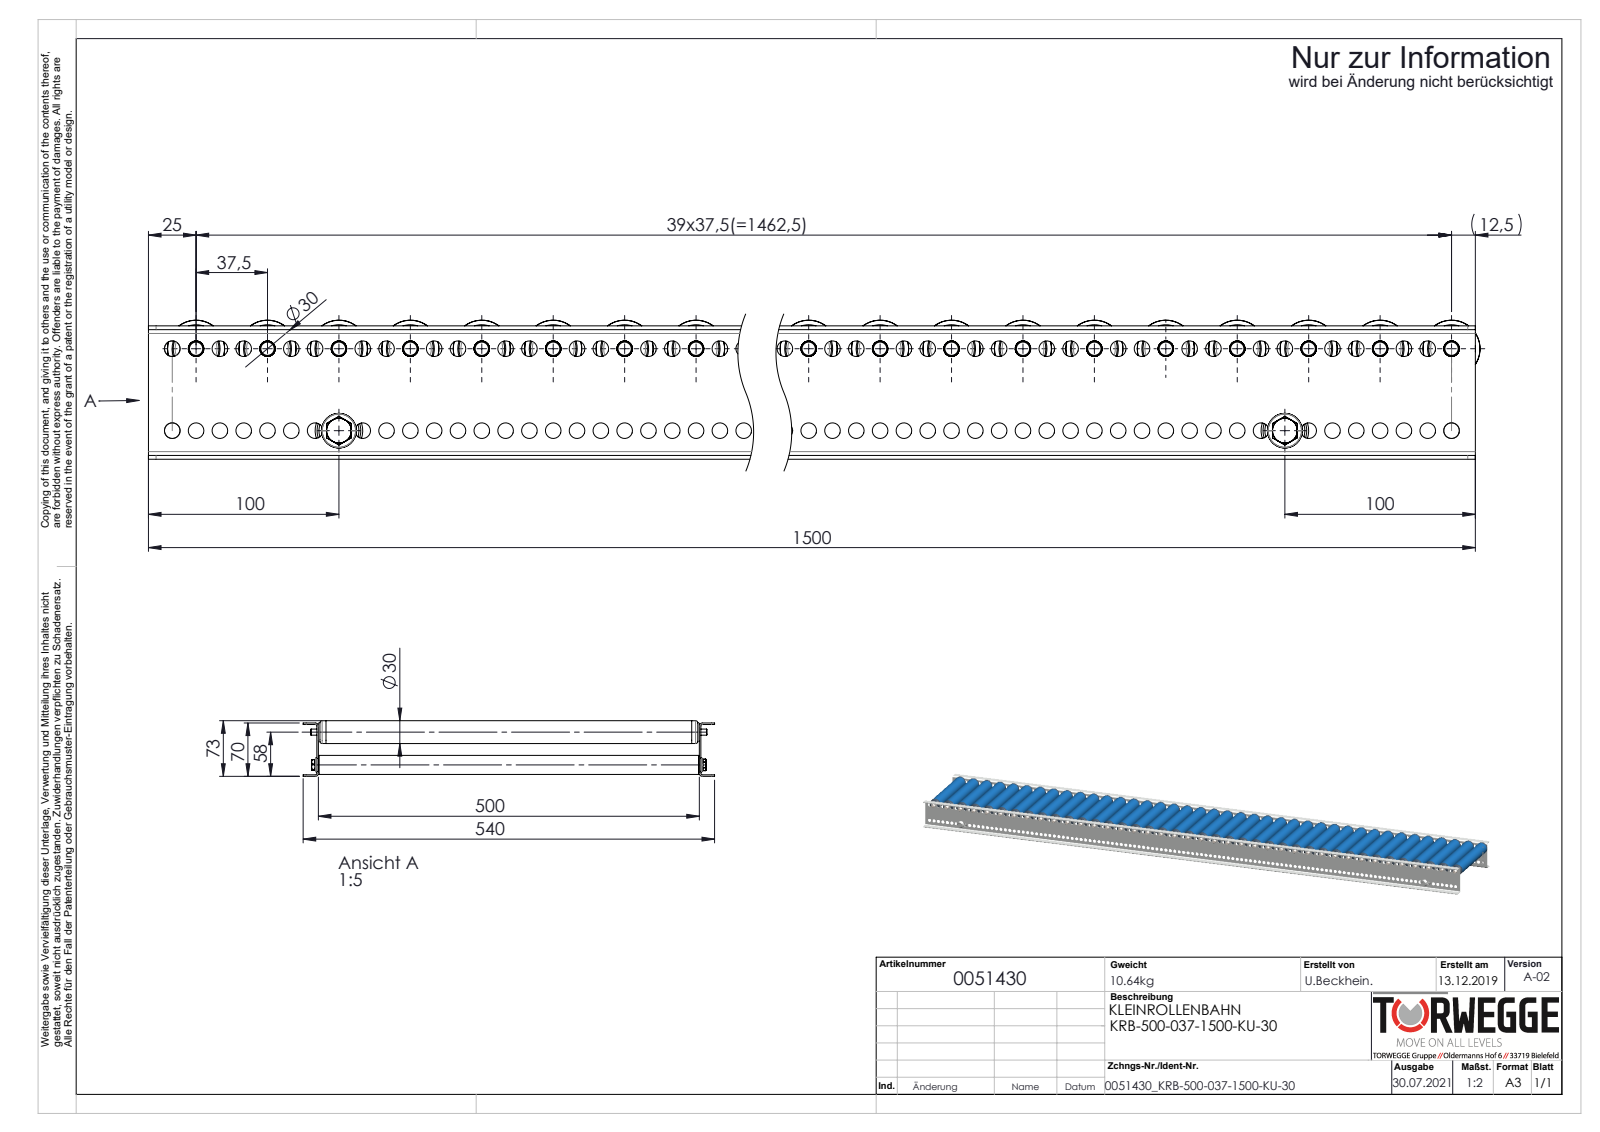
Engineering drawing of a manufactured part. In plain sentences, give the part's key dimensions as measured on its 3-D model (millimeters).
The part is named "0039778-Achse-ST-Ø08-KFG_AL520-G-FA; S100994_Sperrzahnschraube_M08x16-8.8-A2K; S100995_TYP-KUT50-30x1,8-A8; Traversen_KFG_L500 (+4 more)". Its 3-D file was written by "SolidWorks 2020 (AUTOMOTIVE_DESIGN)". It is 92 solids with 9472 faces: 2920 planar, 3568 cylindrical and 2984 other. Overall it measures 1502.5 by 540 by 73 millimeters. Its volume is 4 850 000 cubic millimeters and its surface area 5 172 000 square millimeters. Round holes: 238 of diameter 8.2, 40 of diameter 8.1, 40 of diameter 22.6, 40 of diameter 25.2, 2 of diameter 6.8, 2 of diameter 21. Round bosses or shafts: 42 of diameter 8, 40 of diameter 30, 40 of diameter 29.9, 40 of diameter 26.5, 40 of diameter 26.4, 40 of diameter 24, 2 of diameter 25. Partial cylindrical surfaces (rounded edges, fillets, slot ends): 40 of radius 5.05, 8 of radius 4, 4 of radius 2. The main face-to-face distances are 2, 502, 500, 68, 504, 70, 66, 10, 490, 492. The hole center spacings are 12.5, 25, 37.5, 50, 62.5, 75, 87.5, 100.
